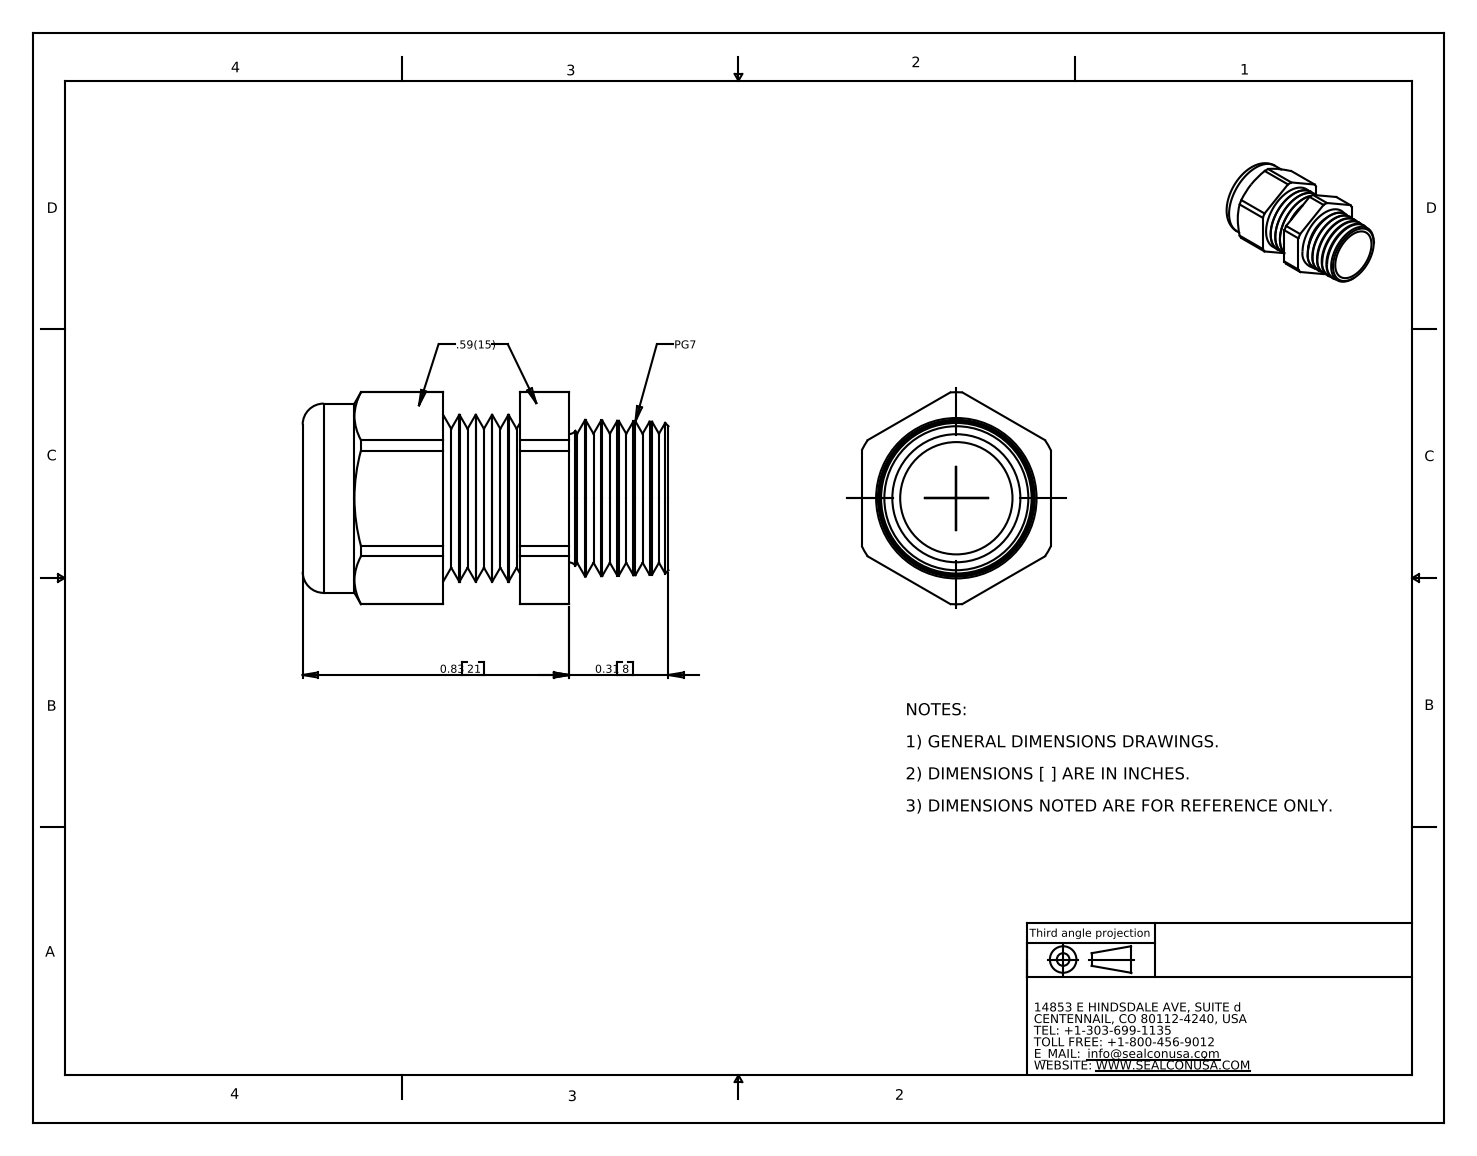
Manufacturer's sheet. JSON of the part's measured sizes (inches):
{"part_name": "CD07AA-BK", "step_written_by": "SolidWorks 2007 (CONFIG_CONTROL_DESIGN)", "units": "inches", "bodies": {"solids": 2, "faces": 124, "planar": 20, "cylindrical": 32, "other": 72}, "overall_size": [1.14, 0.661, 0.59], "volume_in3": 0.14, "surface_area_in2": 5.059, "round_holes": [[0.35, 1], [0.417, 1]], "round_bosses_or_shafts": [[0.59, 1], [0.519, 1]], "partial_cylinders_radius": [[0.33, 1]], "face_to_face_distances": [0.59, 0.154, 0.238, 0.392, 0.277, 0.515, 0.669, 0.979, 0.702, 0.464]}
